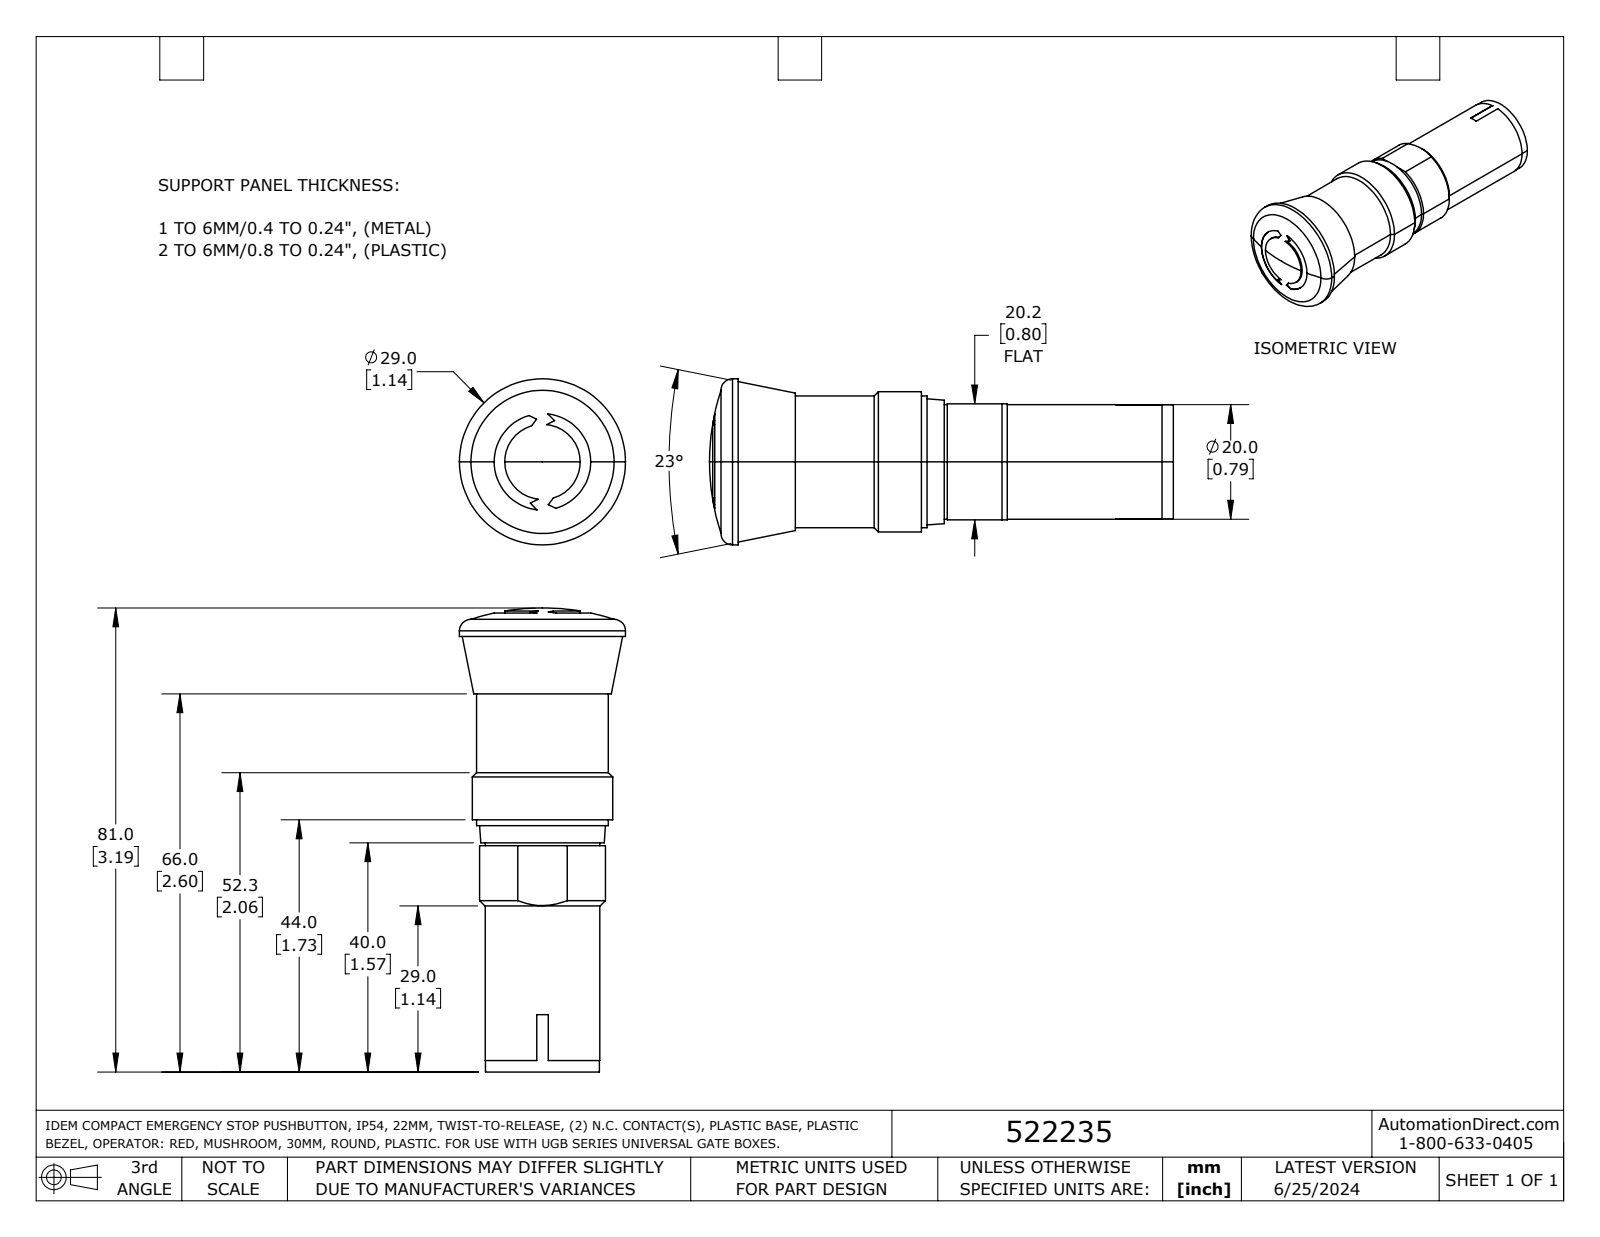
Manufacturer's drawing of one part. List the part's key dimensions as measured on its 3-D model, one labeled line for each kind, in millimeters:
Part name (STEP PRODUCT): 522235
STEP written by: SolidWorks 2023 (AUTOMOTIVE_DESIGN)
Units: millimetres
Bodies: 1 solid, 62 faces (28 planar, 22 cylindrical, 12 other)
Overall size (bounding box): 81 × 29 × 29
Volume: 31 940 mm³ · Surface area: 6 839 mm²
Round holes (diameter × count): ⌀16.9 ×1
Round bosses / shafts (diameter × count): ⌀29 ×1, ⌀24.5 ×1, ⌀23 ×1, ⌀20 ×1, ⌀19.9 ×1
Partial cylindrical surfaces — rounded edges, fillets, slot ends (radius × count): R6.6 ×2, R11 ×1
Main face-to-face distances: 20.2, 80, 36, 44, 40.5, 4.5, 39.5, 40, 4, 0.5
